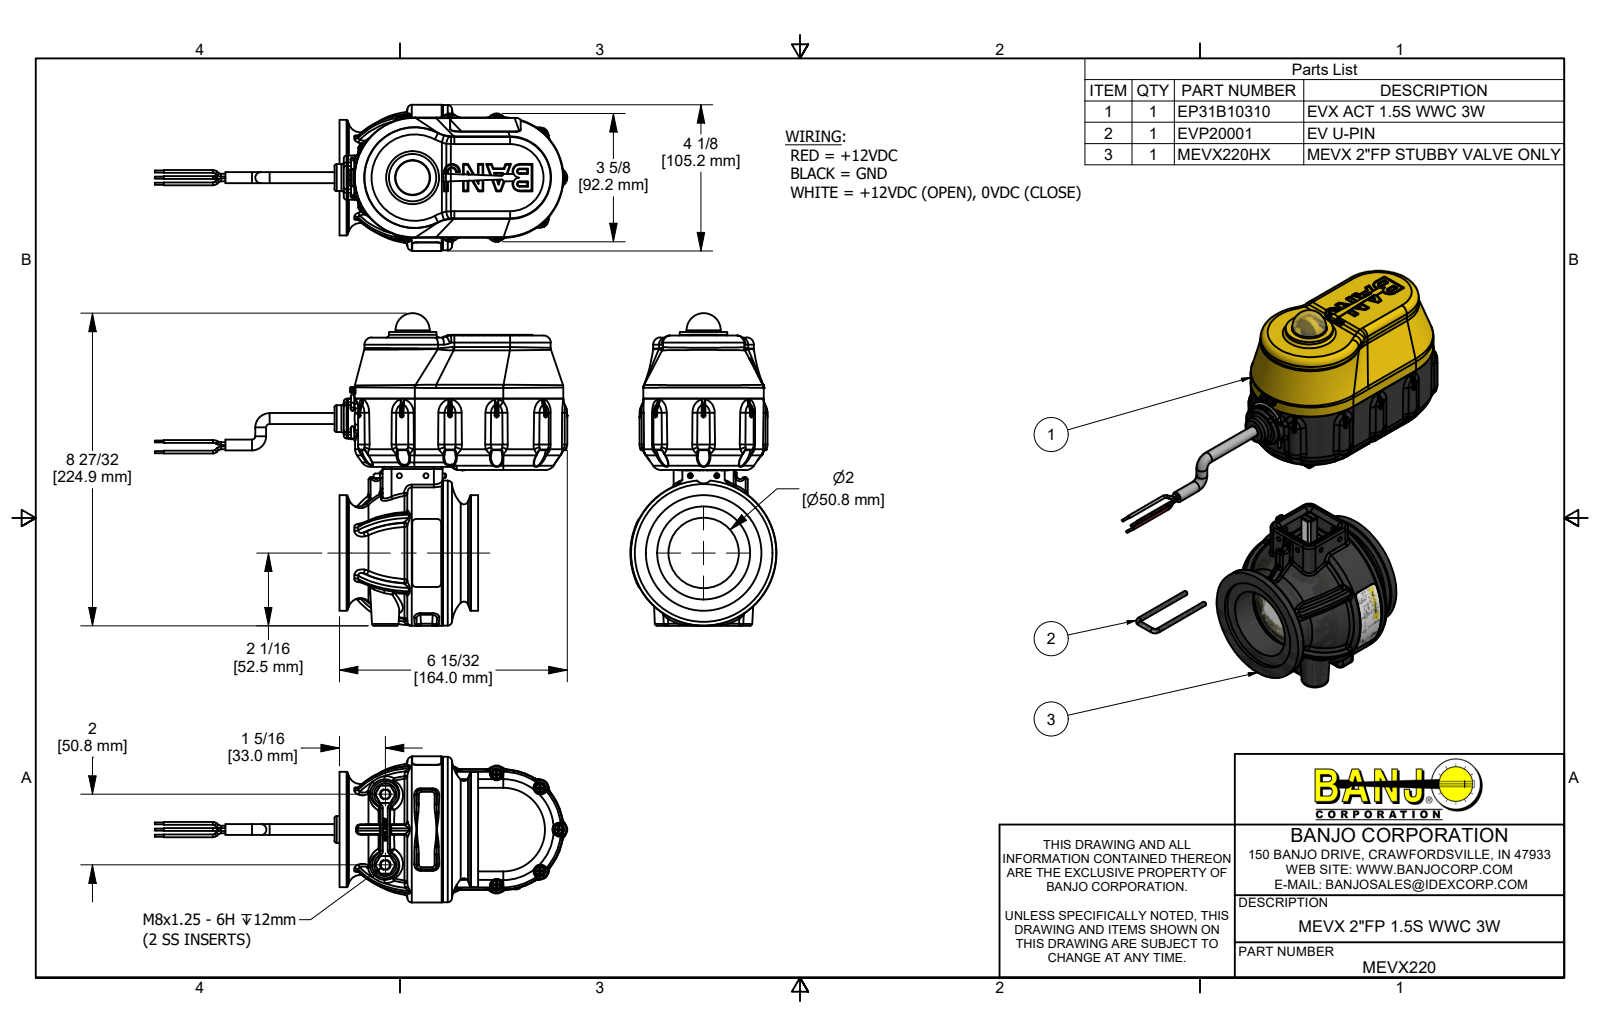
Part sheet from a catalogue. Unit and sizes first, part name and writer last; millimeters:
Units: millimetres
Overall size (bounding box): 296.8 × 224.9 × 105.2
Round holes (diameter × count): ⌀2.4 ×11, ⌀3.8 ×11, ⌀2 ×7, ⌀3.4 ×5, ⌀2.7 ×4, ⌀3.2 ×4, ⌀3.5 ×4, ⌀3.8 ×4, ⌀3.8 ×4, ⌀4.3 ×4, ⌀2.7 ×2, ⌀3 ×2
Round bosses / shafts (diameter × count): ⌀6.4 ×17, ⌀2 ×15, ⌀3.6 ×11, ⌀2.7 ×11, ⌀2.2 ×11, ⌀1.5 ×6, ⌀6.9 ×4, ⌀5.6 ×4
Partial cylindrical surfaces — rounded edges, fillets, slot ends (radius × count): R0.3 ×180, R1 ×145, R0.3 ×92, R0.5 ×71, R0.1 ×53, R0.8 ×34, R1.5 ×31, R2 ×28
Main face-to-face distances: 2.5, 65.2, 1.5, 5.4, 3.8, 48.2, 46.6, 42.8, 14.5, 16
Hole centre spacings: 56.4, 32.6, 68.3, 69, 42.2, 45.1, 69.3, 96.2
Volume: 870 500 mm³ · Surface area: 391 400 mm²
Bodies: 84 solids, 10801 faces (2803 planar, 3097 cylindrical, 4901 other)
Part name (STEP PRODUCT): MEVX220; EP31B10310; B61905PPHS; B632038PM (+8 more)
STEP written by: Autodesk Inventor 2019 (AUTOMOTIVE_DESIGN)
